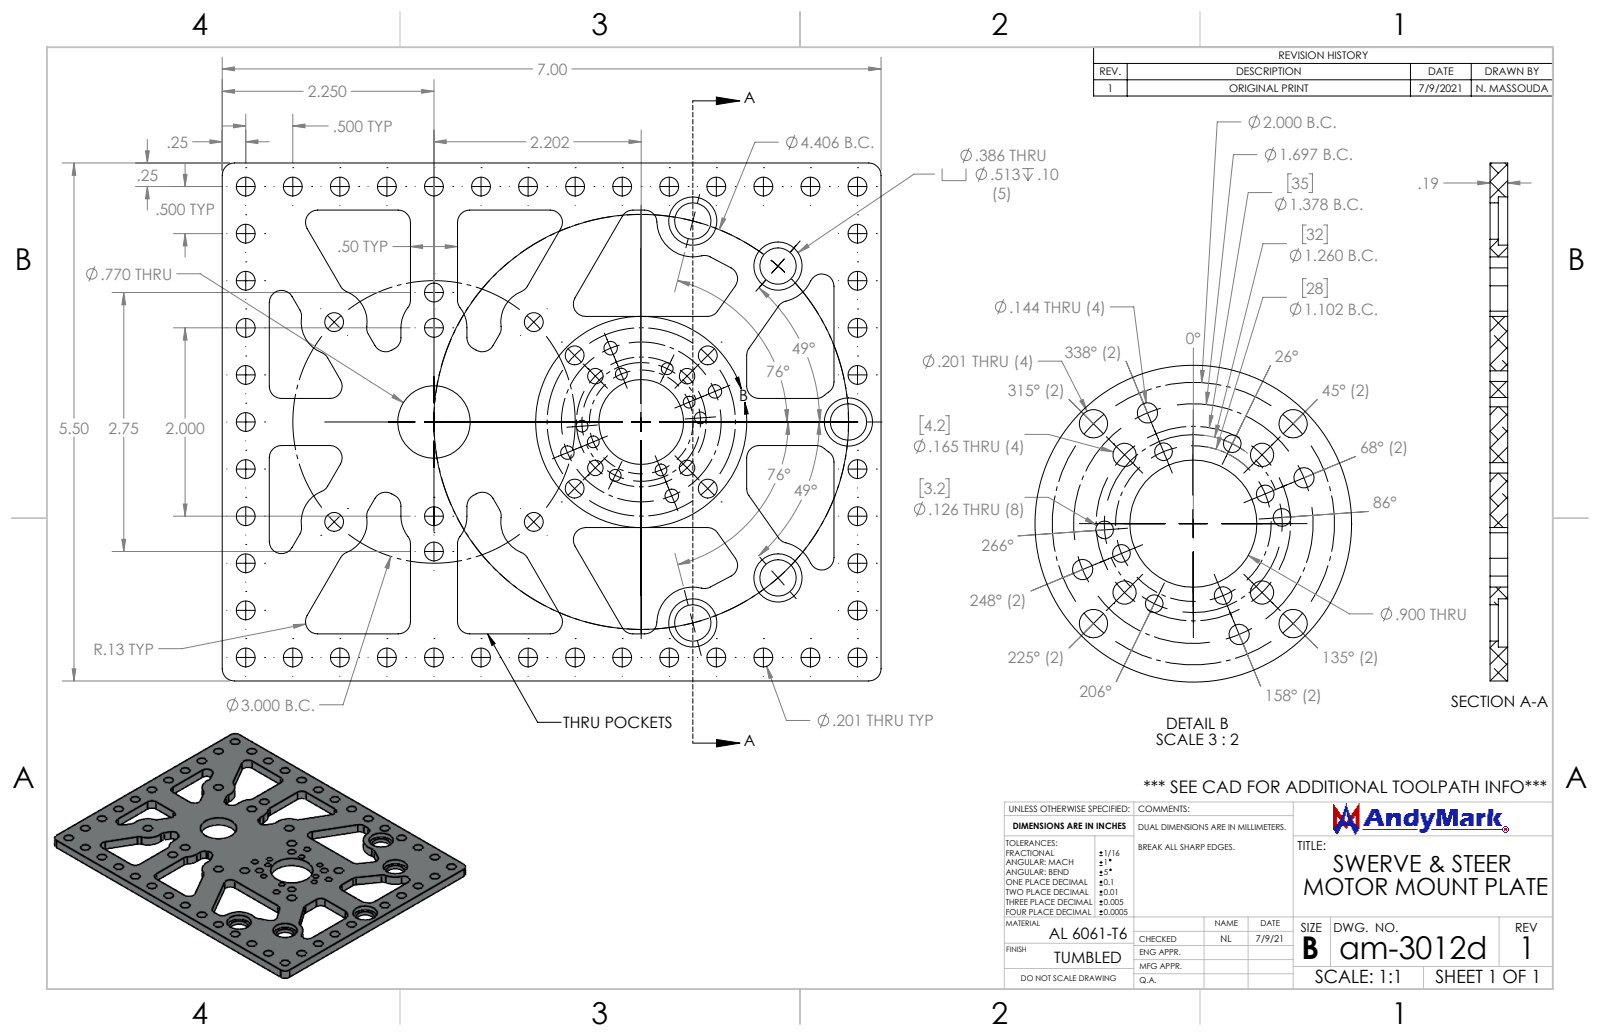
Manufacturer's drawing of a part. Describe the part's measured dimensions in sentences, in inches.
The part is named "am-3012d Swerve and Steer Motor Mount Plate". Its 3-D file was written by "SolidWorks 2021 (CONFIG_CONTROL_DESIGN)". It is 1 solid with 320 faces: 57 planar, 263 cylindrical and 0 other. Overall it measures 7 by 5.5 by 0.188 inches. Its volume is 4.648 cubic inches and its surface area 72.88 square inches. Round holes: 57 of diameter 0.201, 8 of diameter 0.126, 5 of diameter 0.386, 5 of diameter 0.513, 4 of diameter 0.144, 4 of diameter 0.165, 1 of diameter 0.77, 1 of diameter 0.9. Partial cylindrical surfaces (rounded edges, fillets, slot ends): 66 of radius 0.13, 6 of radius 0.351, 5 of radius 0.381, 1 of radius 0.885. The main face-to-face distances are 0.187, 0.5, 5.5, 2.5, 2, 5, 7, 4.5, 6.5, 1.629. The hole center spacings are 1.012, 2, 1, 0.297, 0.39, 1.035, 1.2, 1.414.
